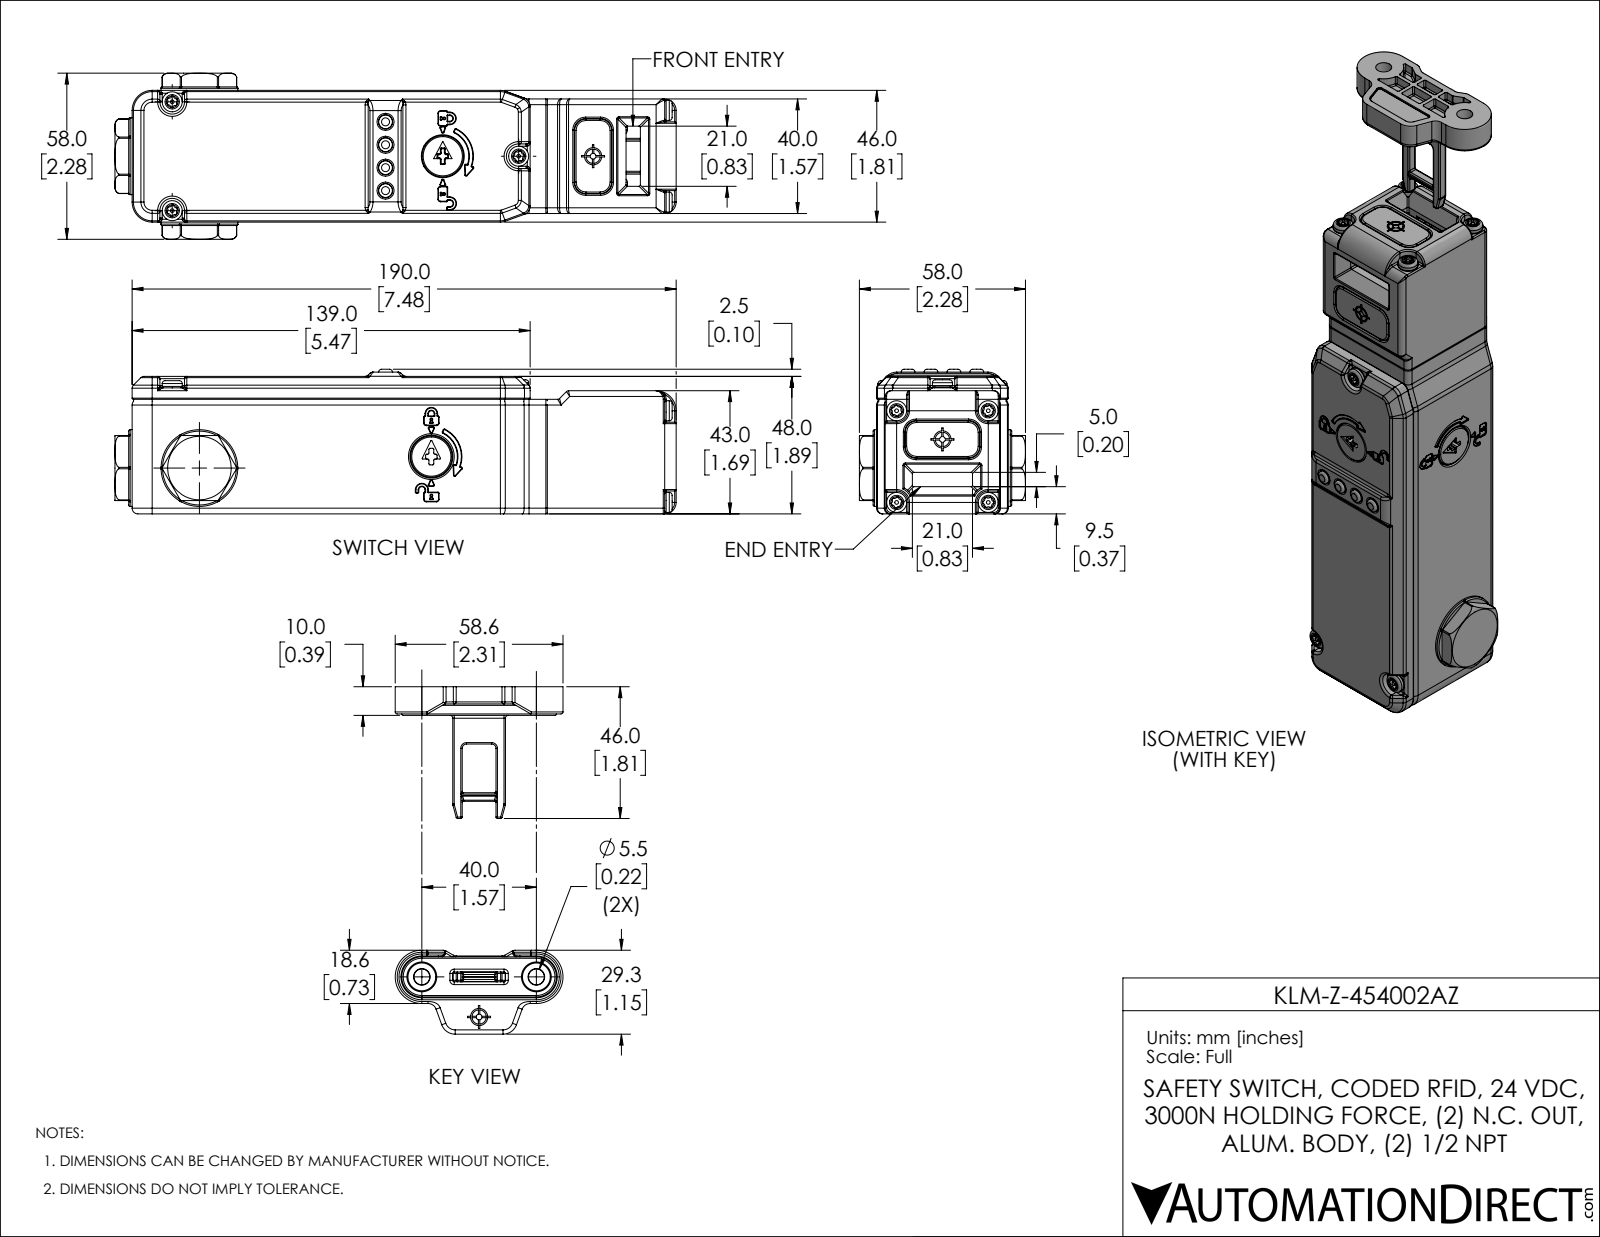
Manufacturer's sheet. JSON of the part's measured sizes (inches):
{"part_name": "454-KLM-Z-AZ", "step_written_by": "SolidWorks 2019 (AUTOMOTIVE_DESIGN)", "units": "inches", "bodies": {"solids": 5, "faces": 3491, "planar": 1020, "cylindrical": 1418, "other": 1053}, "overall_size": [9.724, 2.307, 1.988], "volume_in3": 20.27, "surface_area_in2": 128, "round_holes": [[0.157, 6], [0.236, 6], [0.098, 4], [0.177, 4], [0.197, 4], [0.146, 3], [0.165, 3], [0.13, 2], [0.217, 2], [0.22, 2], [0.591, 2], [0.079, 1]], "round_bosses_or_shafts": [[0.276, 7], [0.138, 7], [0.051, 7], [0.189, 4], [1.055, 2], [0.764, 2], [0.709, 2], [0.571, 2]], "partial_cylinders_radius": [[0.02, 409], [0.012, 105], [0.039, 102], [0.008, 97], [0.079, 50], [0.031, 34], [0.059, 27], [0.157, 27]], "face_to_face_distances": [0.118, 1.693, 1.811, 1.89, 0.098, 0.228, 1.661, 0.13, 1.791, 1.575], "hole_center_spacings": [0.319, 0.481, 0.63, 0.748, 1.043, 1.043, 1.081, 1.26]}
